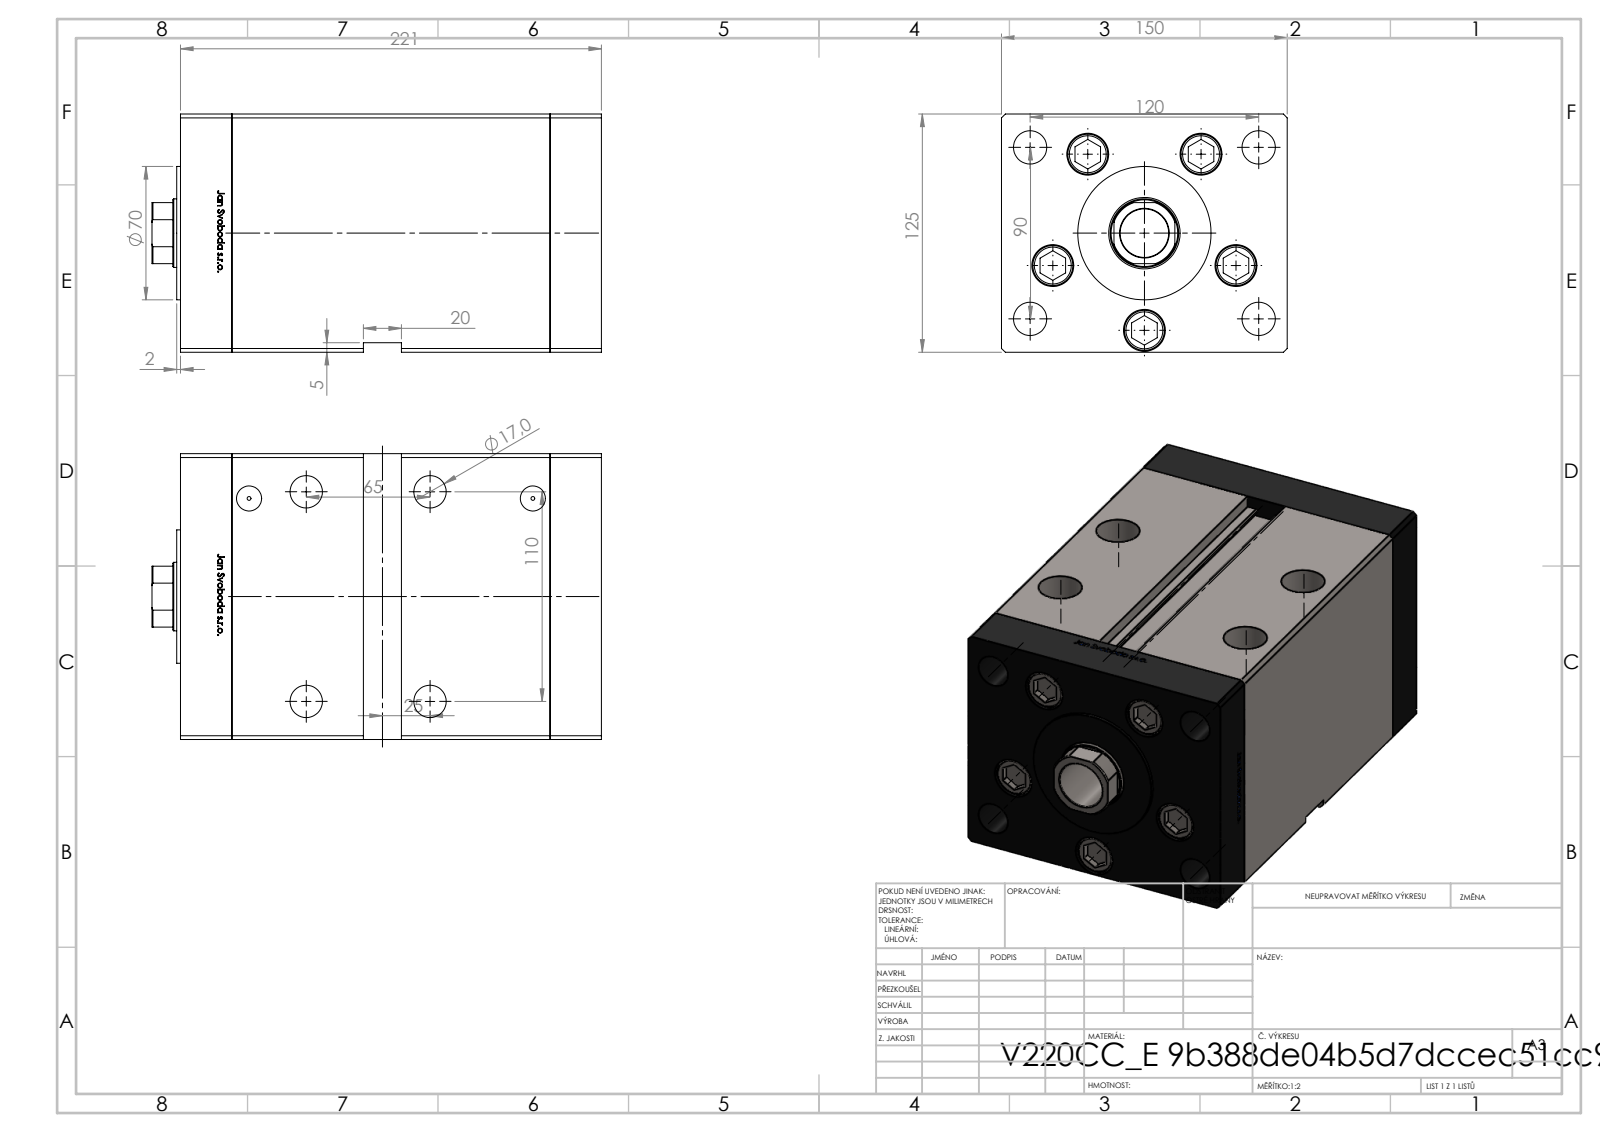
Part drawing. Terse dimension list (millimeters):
name: V220C_FRONT_E; V220C BACK_E; V220C_E MIDDLE; V220C_VC_E (+1 more)
written by: SolidWorks 2019 (CONFIG_CONTROL_DESIGN)
unit: mm
bodies: 14 solids, 1214 faces (475 planar, 165 cylindrical, 574 other)
size: 236 × 150 × 125
volume: 3 421 000 mm³; area: 396 942 mm²
holes: 9× ⌀17.5, 5× ⌀22, 4× ⌀17, 4× ⌀23, 2× ⌀2, 2× ⌀13.16, 1× ⌀25.5, 1× ⌀36, 1× ⌀37.5
bosses: 5× ⌀21, 5× ⌀8, 1× ⌀80, 1× ⌀70
rounds: 2× R0.93, 1× R17.5
face distances: 27, 194, 167, 125, 150, 33.5, 6.5, 221, 160.5, 187.5
hole spacings: 51, 75, 30.43, 30.48, 58.89, 60.3, 61.25, 63.14
